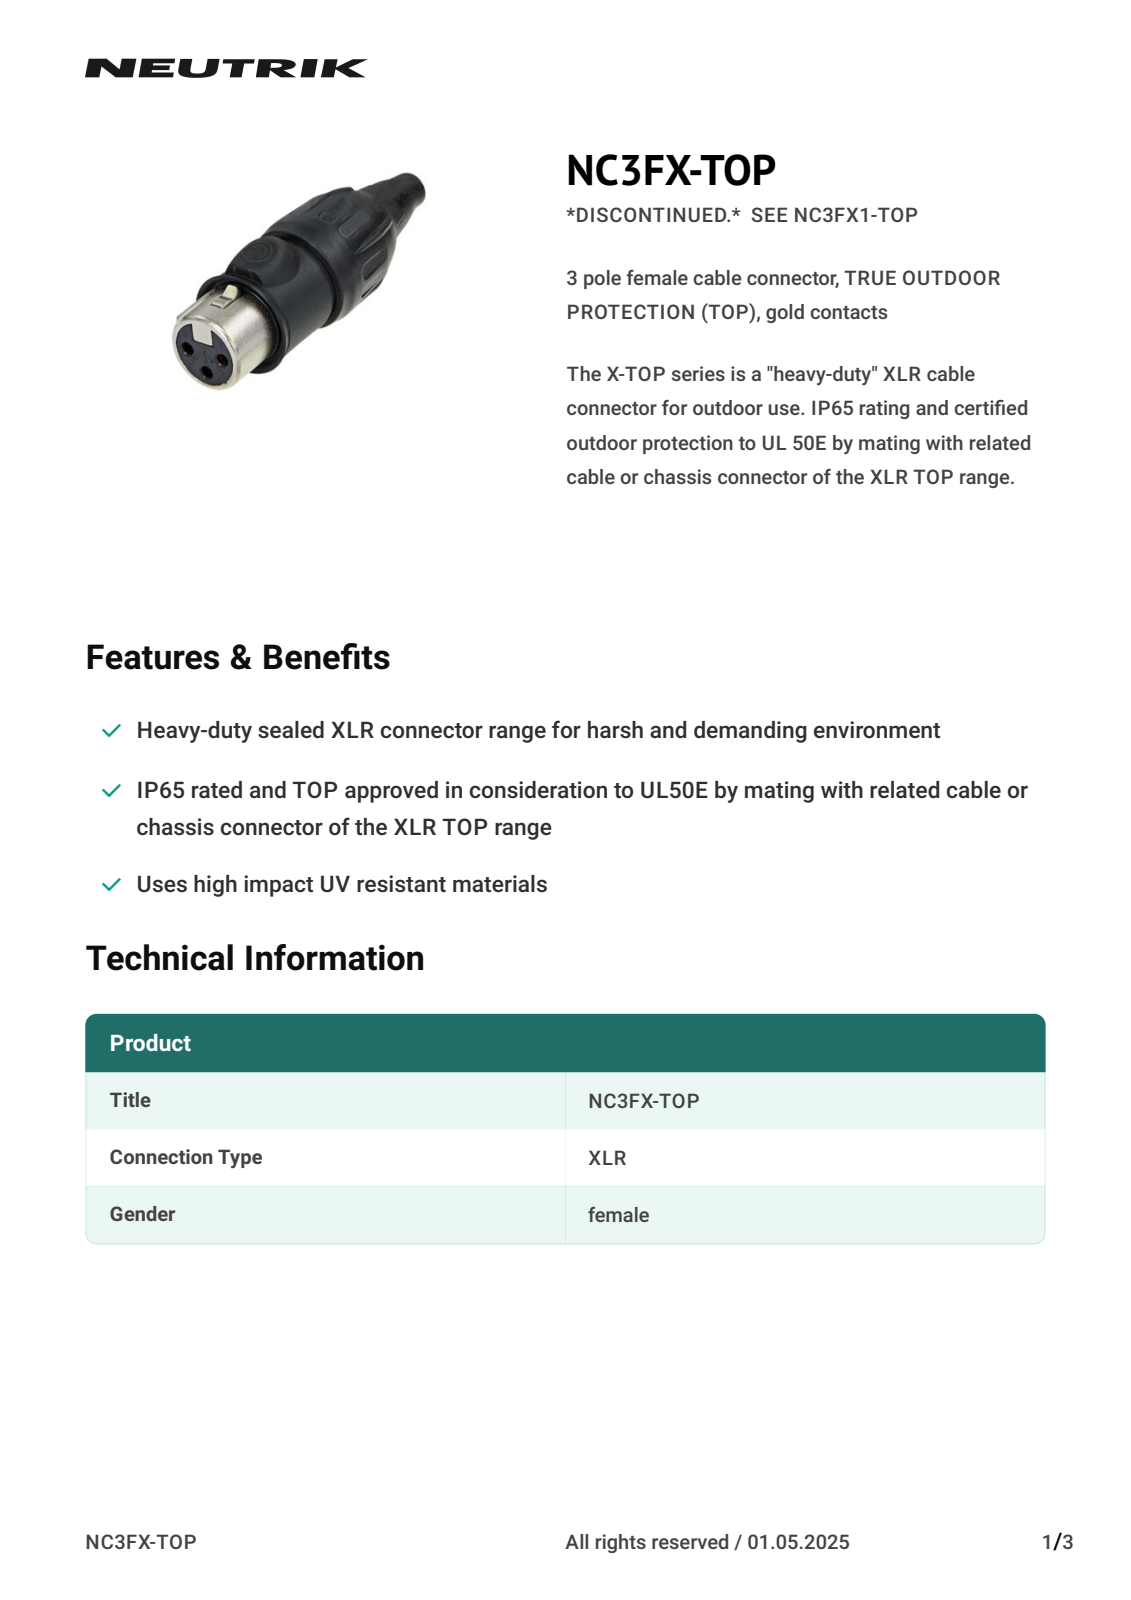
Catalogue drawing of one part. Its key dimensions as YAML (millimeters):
part_name: "NC3FX-TOP"
step_written_by: "CREO PARAMETRIC BY PTC INC, 2021184 (AUTOMOTIVE_DESIGN)"
units: millimeters
bodies: {solids: 1, faces: 1145, planar: 591, cylindrical: 97, other: 457}
overall_size: [70.75, 24.4, 22.6]
volume: 17636
surface_area: 4741
round_holes:
  - {diameter: 2.5, count: 3}
  - {diameter: 2.55, count: 3}
  - {diameter: 5.13, count: 1}
  - {diameter: 13, count: 1}
round_bosses_or_shafts:
  - {diameter: 22.6, count: 1}
  - {diameter: 19.35, count: 1}
  - {diameter: 15.75, count: 1}
  - {diameter: 6, count: 1}
partial_cylinders:
  - {radius: 1, count: 14}
  - {radius: 0.22, count: 9}
  - {radius: 0.2, count: 2}
  - {radius: 0.75, count: 2}
  - {radius: 0.3, count: 1}
  - {radius: 0.5, count: 1}
  - {radius: 1.59, count: 1}
  - {radius: 2.02, count: 1}
face_to_face_distances: [29.4, 29.2, 70.71, 70.51, 41.31, 5.36, 5.16, 24.04, 65.35, 0.58]
hole_center_spacings: [4.05, 5.66, 3.95, 8.1]
